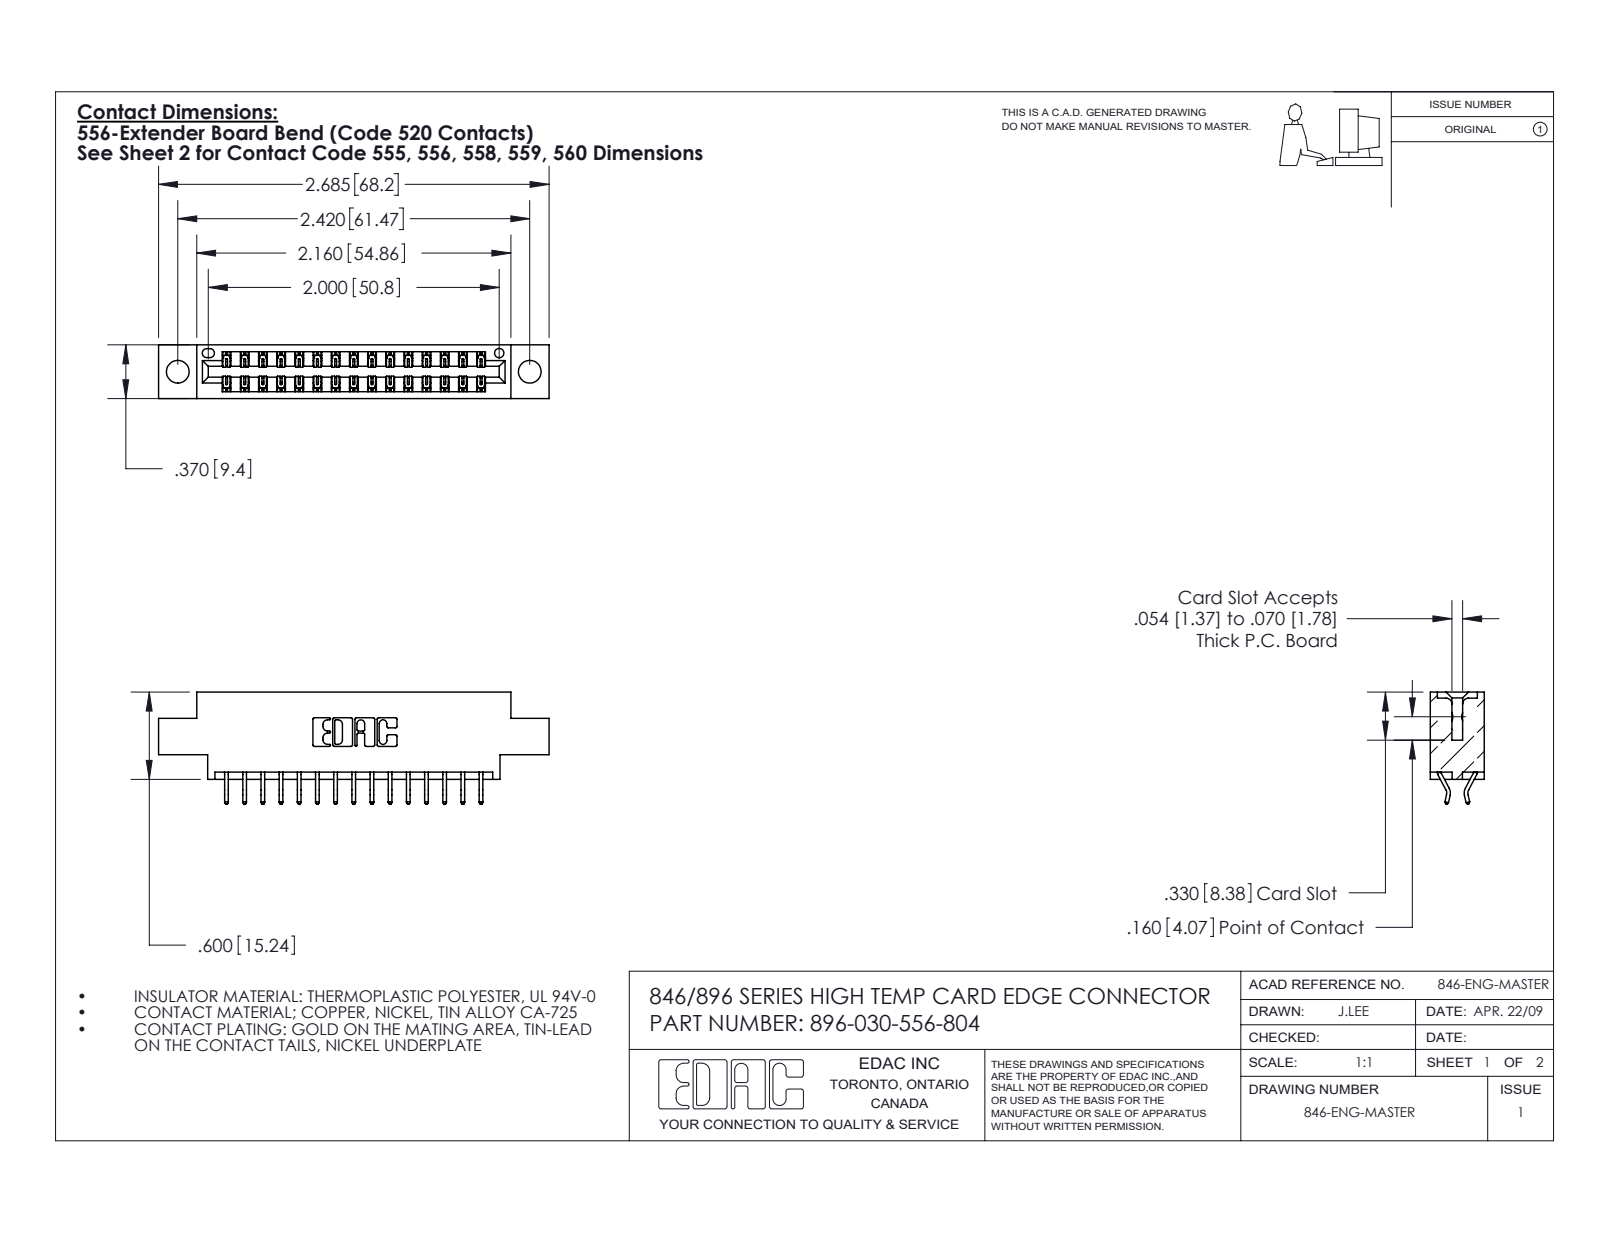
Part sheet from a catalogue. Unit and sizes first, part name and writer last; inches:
Units: inches
Overall size (bounding box): 2.685 × 0.77 × 0.37
Round holes (diameter × count): ⌀0.156 ×2, ⌀0.064 ×1
Partial cylindrical surfaces — rounded edges, fillets, slot ends (radius × count): R0.006 ×45, R0.01 ×22, R0.007 ×6, R0.031 ×6, R0.026 ×3, R0.01 ×2, R0.014 ×2, R0.022 ×2
Main face-to-face distances: 0.048, 0.322, 0.37, 0.25, 0.025, 0.072, 0.298, 0.275, 0.148, 0.222
Hole centre spacings: 0.246, 2.213, 2.42
Volume: 0.378 in³ · Surface area: 12.49 in²
Bodies: 31 solids, 1866 faces (1250 planar, 616 cylindrical, 0 other)
Part name (STEP PRODUCT): 346 Part_0.170 Offset - 0.156 Dia-TH; 396-030-556-804; 345-292-001_556 Tail
STEP written by: SolidWorks 2016 (CONFIG_CONTROL_DESIGN)
